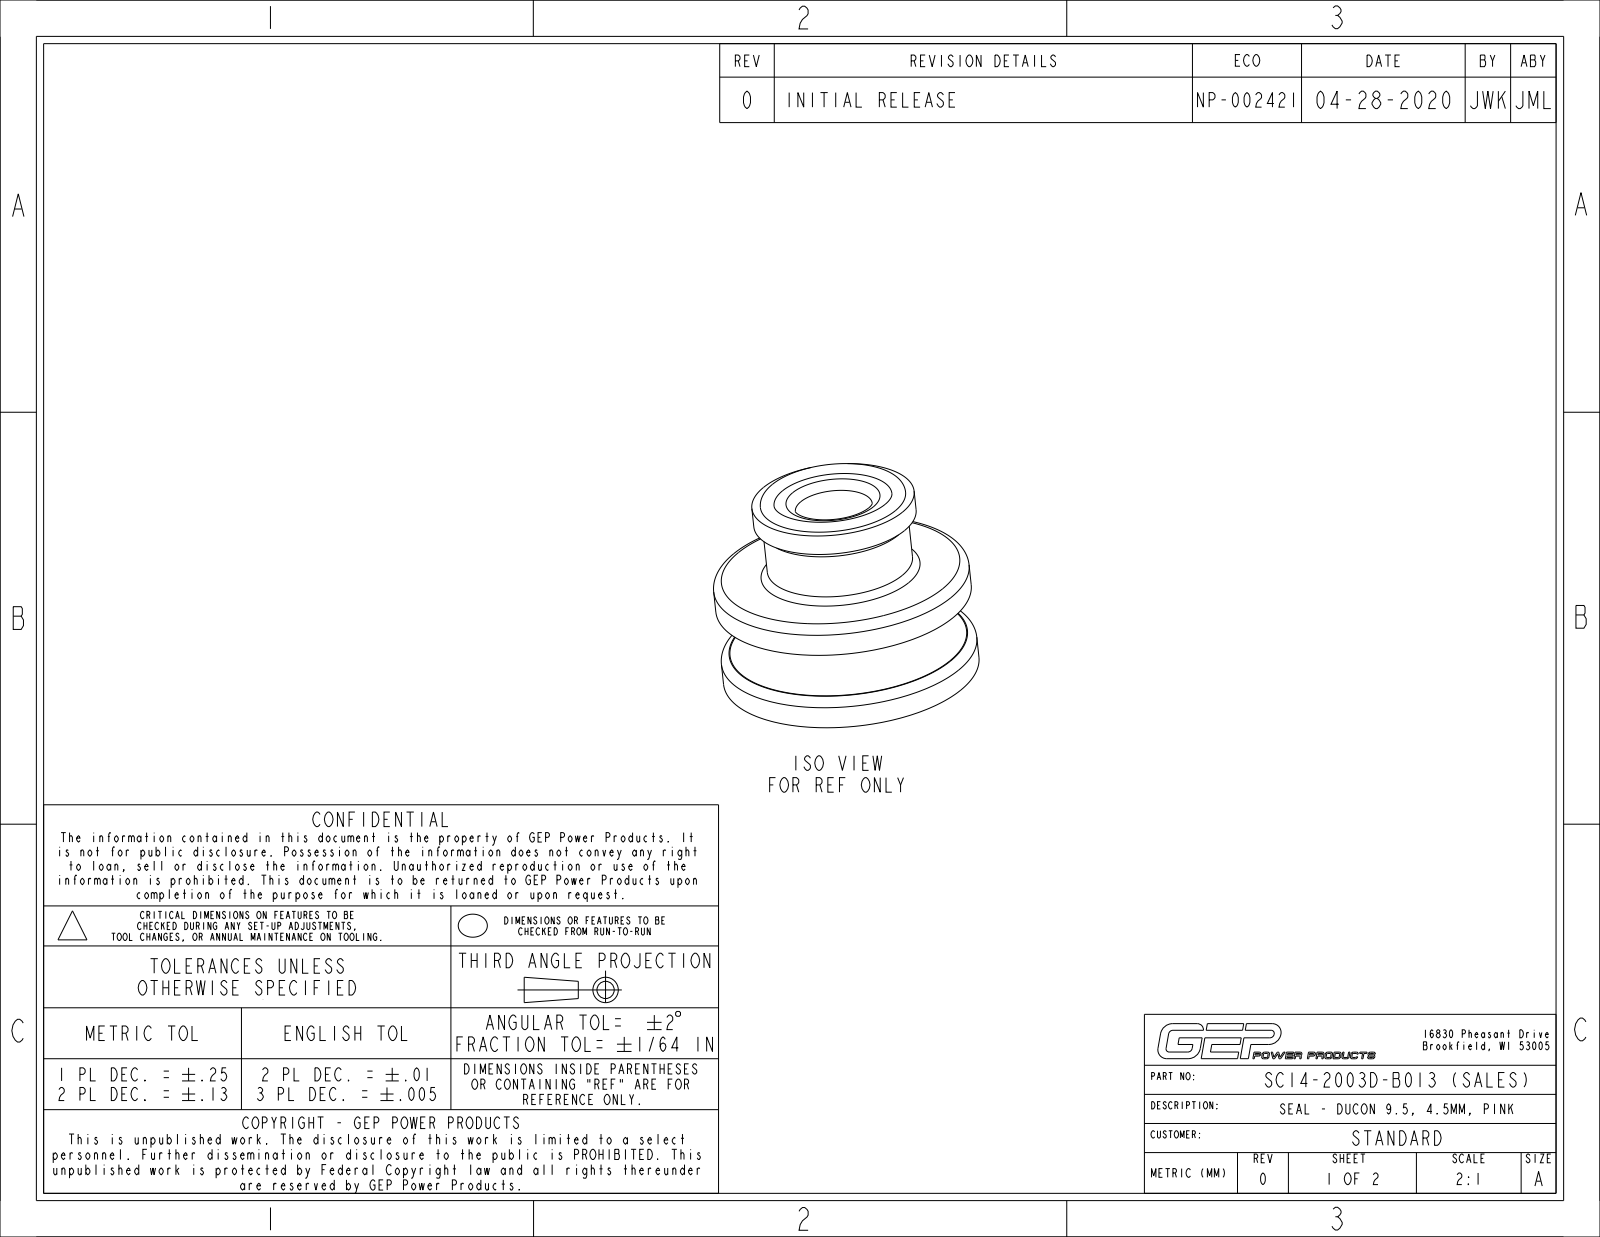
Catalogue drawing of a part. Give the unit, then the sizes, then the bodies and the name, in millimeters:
Units: millimetres
Overall size (bounding box): 14.95 × 14.95 × 12.1
Round holes (diameter × count): ⌀4.5 ×1
Round bosses / shafts (diameter × count): ⌀14.95 ×1, ⌀9.5 ×1, ⌀8.5 ×1
Main face-to-face distances: 6.5, 11.1, 4.6, 1.8, 4.7, 6.4, 9.9, 5.2, 3.4, 1.2
Volume: 1 039 mm³ · Surface area: 1 035 mm²
Bodies: 1 solid, 88 faces (42 planar, 10 cylindrical, 36 other)
Part name (STEP PRODUCT): PC14-2003D-B013_NCF; SC14-2003D-B013_NCF_ASM
STEP written by: CREO PARAMETRIC BY PTC INC, 2017110 (CONFIG_CONTROL_DESIGN)
